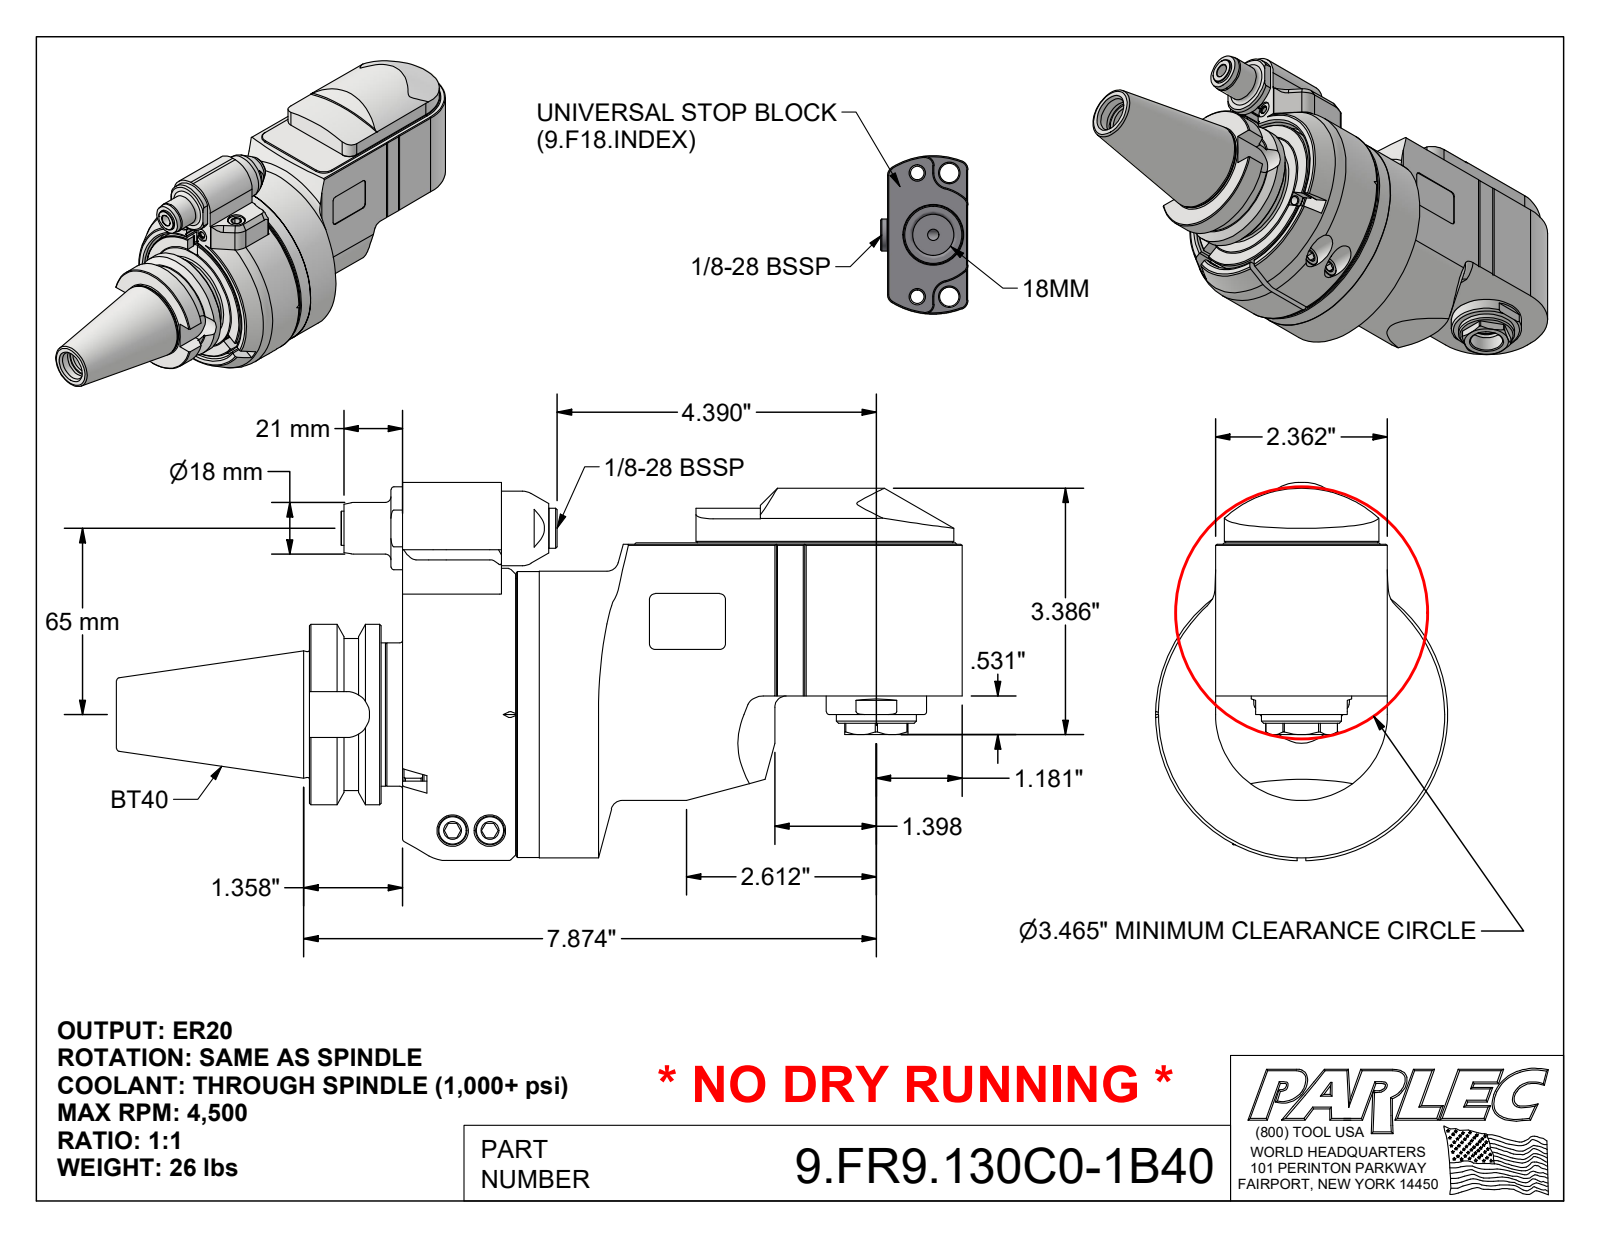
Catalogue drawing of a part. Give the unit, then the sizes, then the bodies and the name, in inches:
Units: inches
Overall size (bounding box): 11.63 × 5.196 × 4.016
Round holes (diameter × count): ⌀0.165 ×4, ⌀0.256 ×3, ⌀0.315 ×3, ⌀0.102 ×2, ⌀0.13 ×2, ⌀0.409 ×2, ⌀0.433 ×2, ⌀0.807 ×2, ⌀1.142 ×2, ⌀0.118 ×1, ⌀0.157 ×1, ⌀0.197 ×1
Round bosses / shafts (diameter × count): ⌀0.394 ×4, ⌀0.236 ×2, ⌀4.016 ×1, ⌀3.937 ×1, ⌀3.929 ×1, ⌀3.74 ×1, ⌀3.031 ×1, ⌀2.48 ×1
Partial cylindrical surfaces — rounded edges, fillets, slot ends (radius × count): R0.039 ×14, R0.118 ×6, R0.157 ×5, R0.079 ×4, R0.02 ×2, R0.236 ×2, R0.315 ×2, R0.551 ×2
Main face-to-face distances: 2.362, 0.02, 0.276, 0.039, 0.295, 0.315, 0.335, 1.122, 0.118, 1.28
Hole centre spacings: 0.276, 0.504, 0.74, 0.996, 1.916, 0.049, 0.512, 0.551
Volume: 75.52 in³ · Surface area: 202.4 in²
Bodies: 2 solids, 521 faces (234 planar, 147 cylindrical, 140 other)
Part name (STEP PRODUCT): 9.FR9.130C0-1B40; FR90-13C-gearbox only
STEP written by: Autodesk Inventor 2022 (AUTOMOTIVE_DESIGN)
